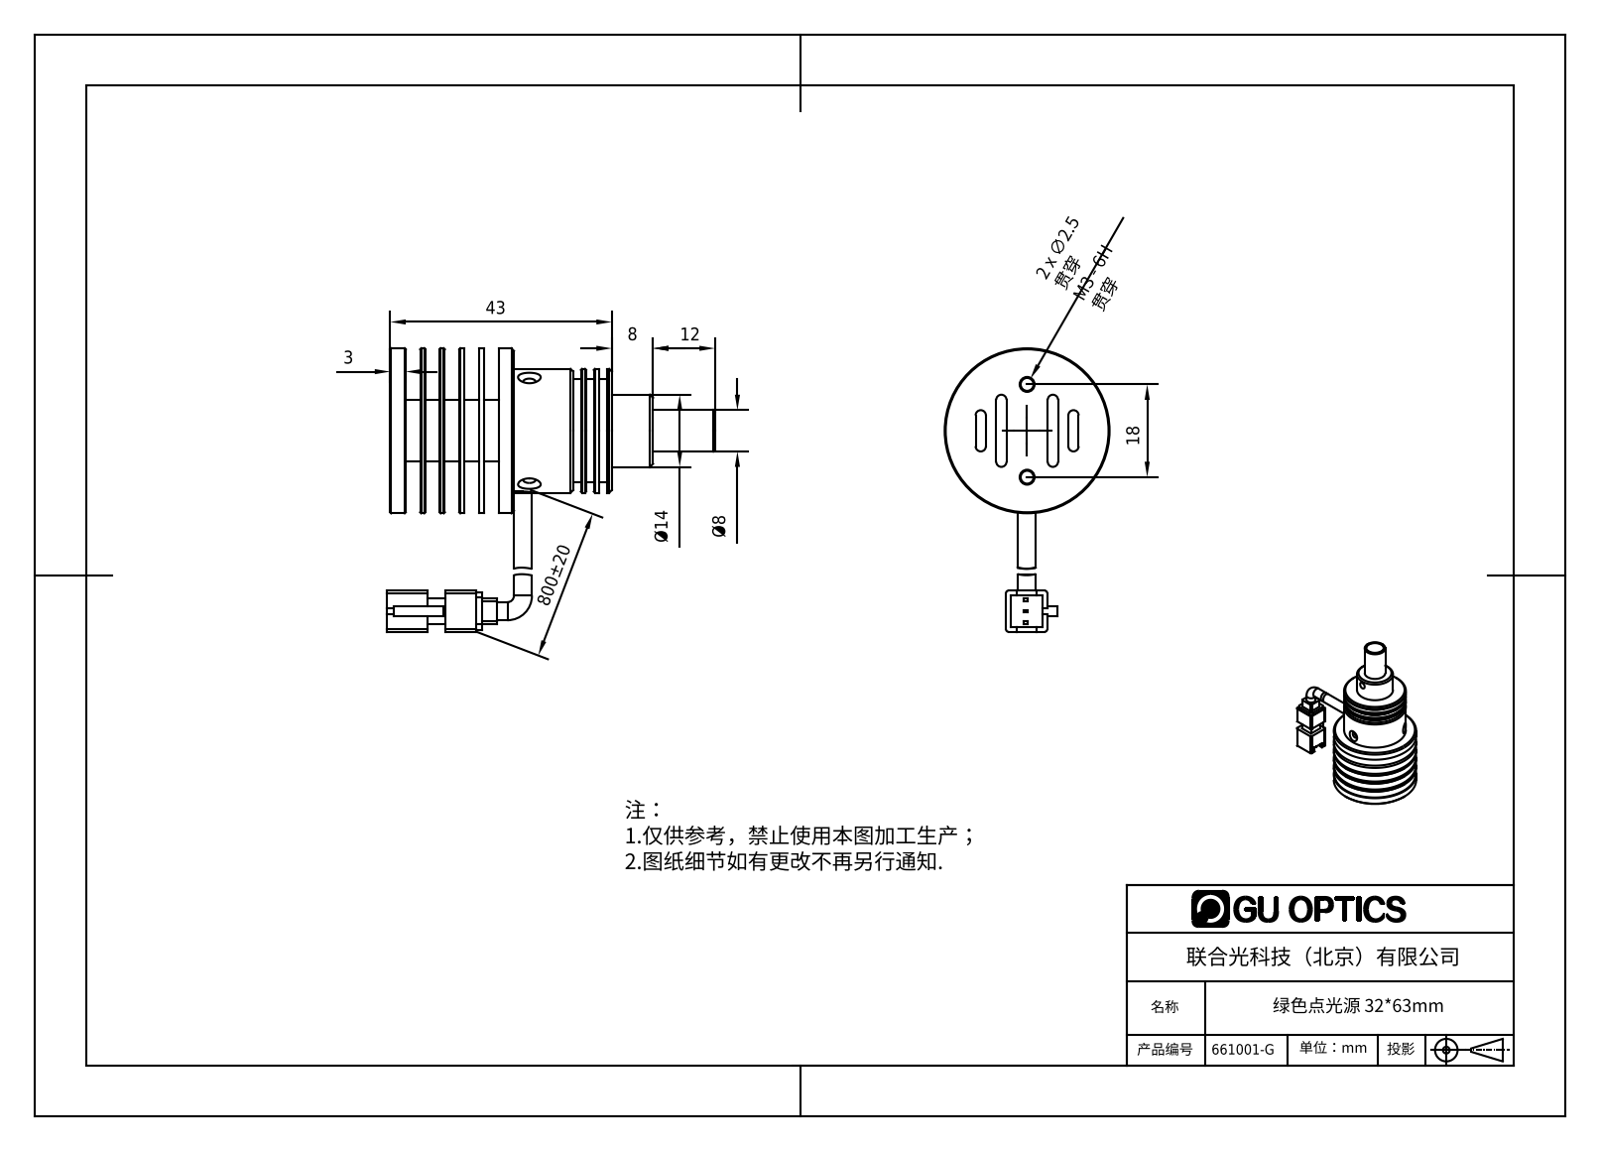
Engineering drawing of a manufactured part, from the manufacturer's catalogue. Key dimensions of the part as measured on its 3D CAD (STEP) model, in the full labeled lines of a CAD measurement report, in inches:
Part name (STEP PRODUCT): 661001-G
STEP written by: SolidWorks 2016 (AUTOMOTIVE_DESIGN)
Units: inches
Bodies: 10 solids, 401 faces (157 planar, 168 cylindrical, 76 other)
Overall size (bounding box): 2.51 × 2.165 × 1.26
Volume: 1.082 in³ · Surface area: 30.54 in²
Round holes (diameter × count): ⌀0.063 ×7, ⌀0.079 ×3, ⌀0.094 ×3, ⌀0.098 ×3, ⌀0.087 ×2, ⌀0.244 ×1, ⌀0.268 ×1, ⌀0.622 ×1, ⌀0.661 ×1, ⌀0.752 ×1, ⌀0.791 ×1
Round bosses / shafts (diameter × count): ⌀0.138 ×2, ⌀1.26 ×1, ⌀0.945 ×1, ⌀0.787 ×1, ⌀0.669 ×1, ⌀0.614 ×1, ⌀0.567 ×1, ⌀0.551 ×1
Partial cylindrical surfaces — rounded edges, fillets, slot ends (radius × count): R0.039 ×12, R0.02 ×8, R0.059 ×3, R0.065 ×1
Main face-to-face distances: 0.15, 0.11, 0.299, 0.039, 0.26, 0.153, 0.303, 0.189, 0.452, 0.409
Hole centre spacings: 0.334, 0.236, 0.251, 0.548, 0.354, 0.473, 0.237, 0.251
